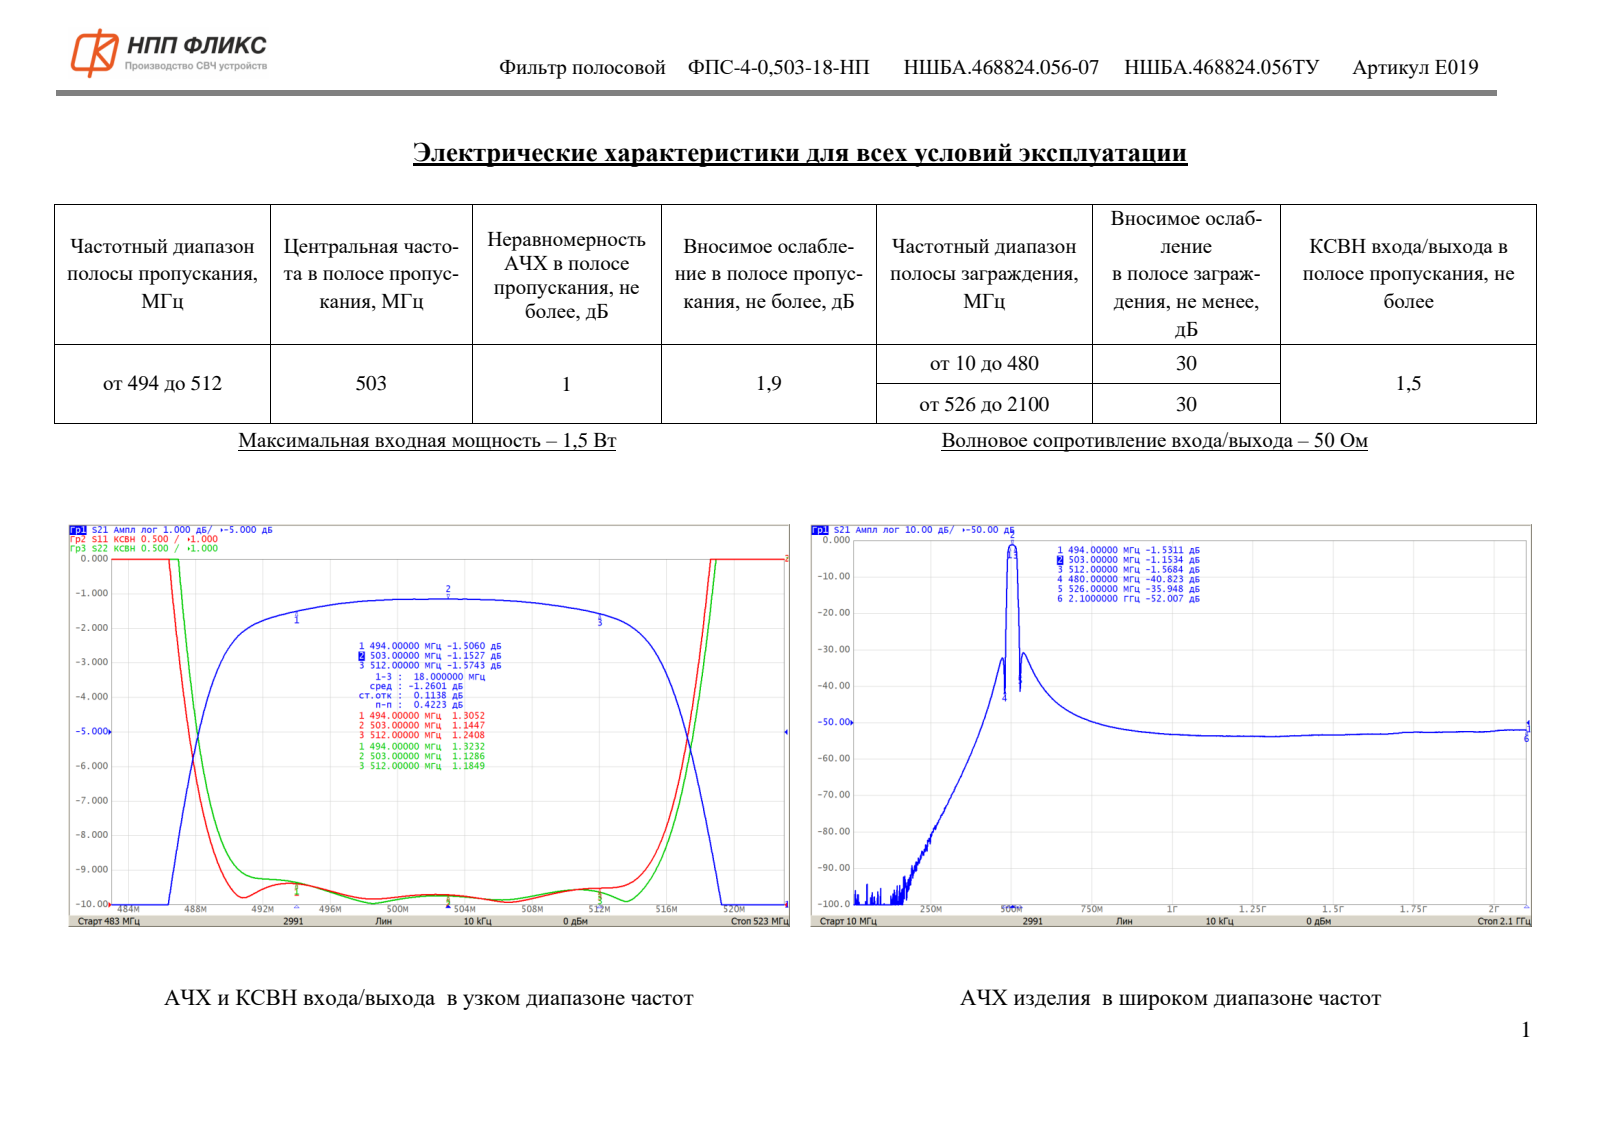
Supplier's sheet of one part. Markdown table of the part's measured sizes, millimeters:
| quantity | value |
| --- | --- |
| part name | НШБА.468824.056-07_Фильтр ФПС-4-0,503-18-НП |
| STEP written by | ASCON Math Kernel (CONFIG_CONTROL_DESIGN) |
| units | millimeters |
| bodies | 1 solid, 771 faces (552 planar, 89 cylindrical, 130 other) |
| overall size | 30 × 25 × 16.91 |
| volume | 1 283 mm³ |
| surface area | 6 133 mm² |
| round holes (diameter × count) | 0.8 × 4, 0.5 × 2 |
| partial cylindrical surfaces (radius × count) | 0.5 × 27, 0.3 × 8, 0.45 × 8, 0.6 × 8, 1 × 8, 0.25 × 1, 0.75 × 1, 0.88 × 1 |
| main face-to-face distances | 22.7, 0.81, 28, 16.91, 16.1, 16.61, 15.8, 22.4, 23, 27.7 |
| hole center spacings | 11.77, 26.64, 21, 22.7, 30.92, 27.2 |
